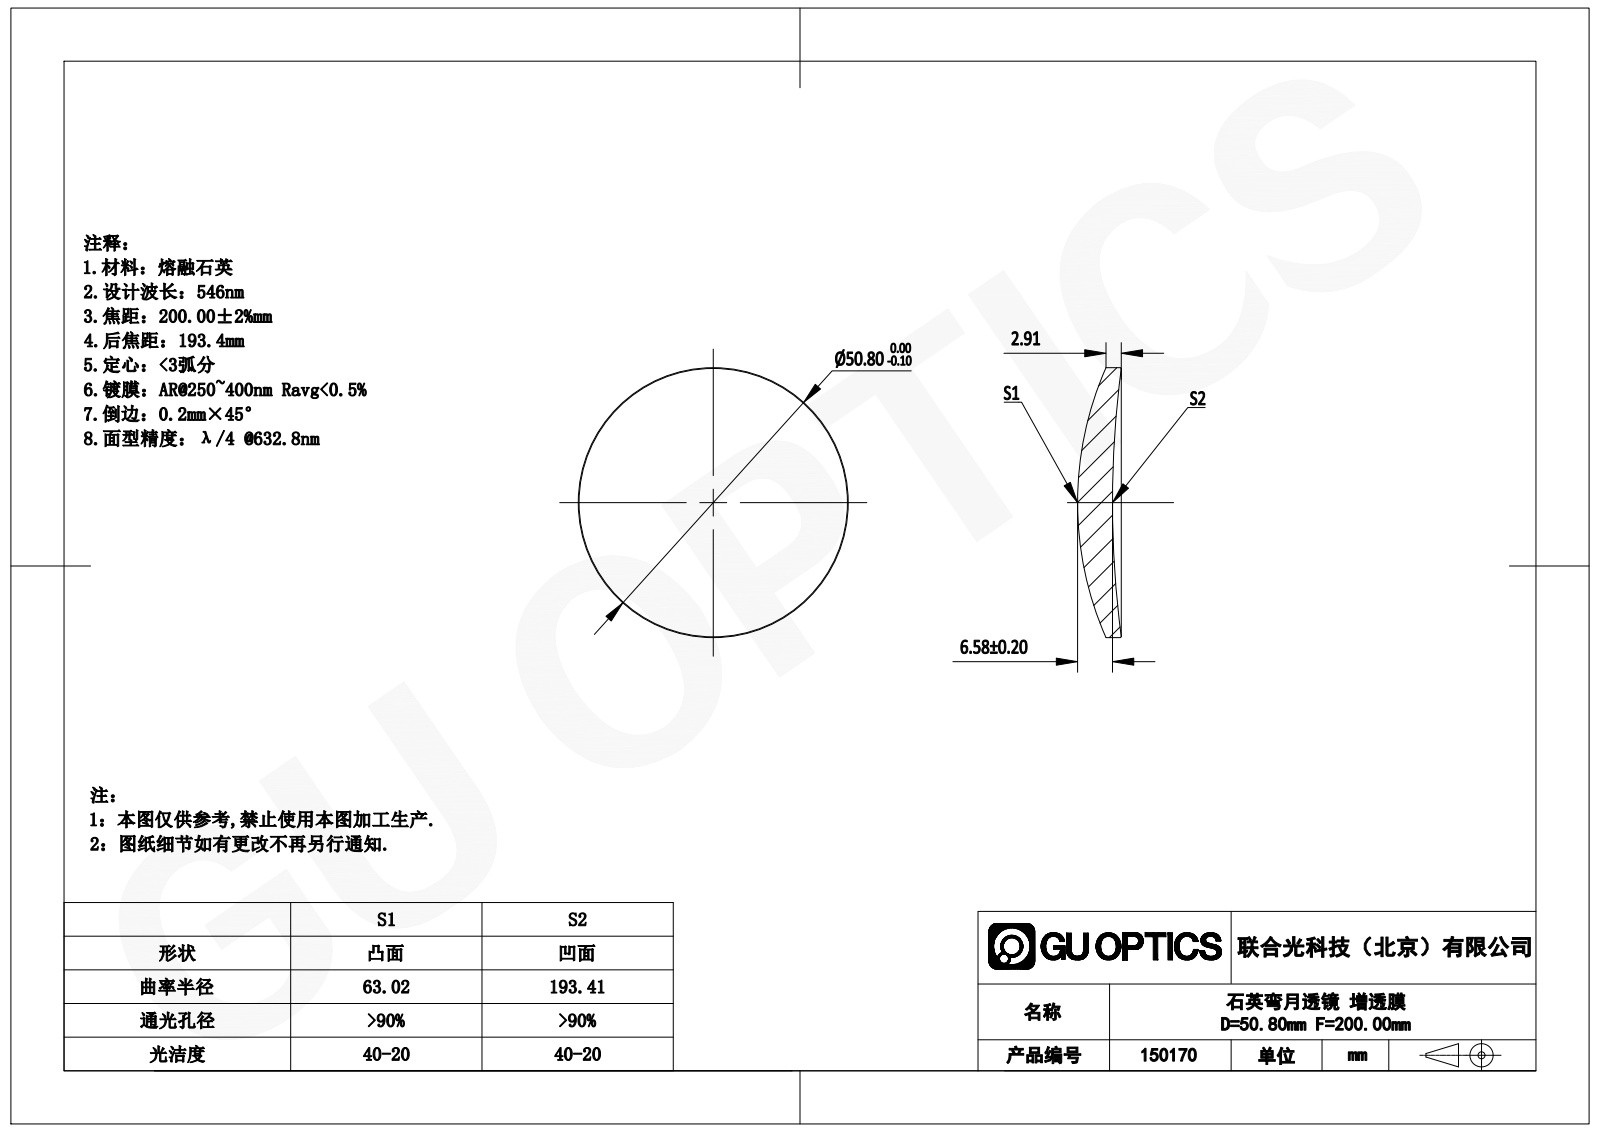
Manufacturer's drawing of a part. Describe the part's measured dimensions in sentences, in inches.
The part is named "GLM2-050B-200-UV". Its 3-D file was written by "SolidWorks 2022 (AUTOMOTIVE_DESIGN)". It is 1 solid with 8 faces: 0 planar, 2 cylindrical and 6 other. Overall it measures 2 by 2 by 0.324 inches. Its volume is 0.59 cubic inches and its surface area 7.122 square inches. Round bosses or shafts: 1 of diameter 2.
